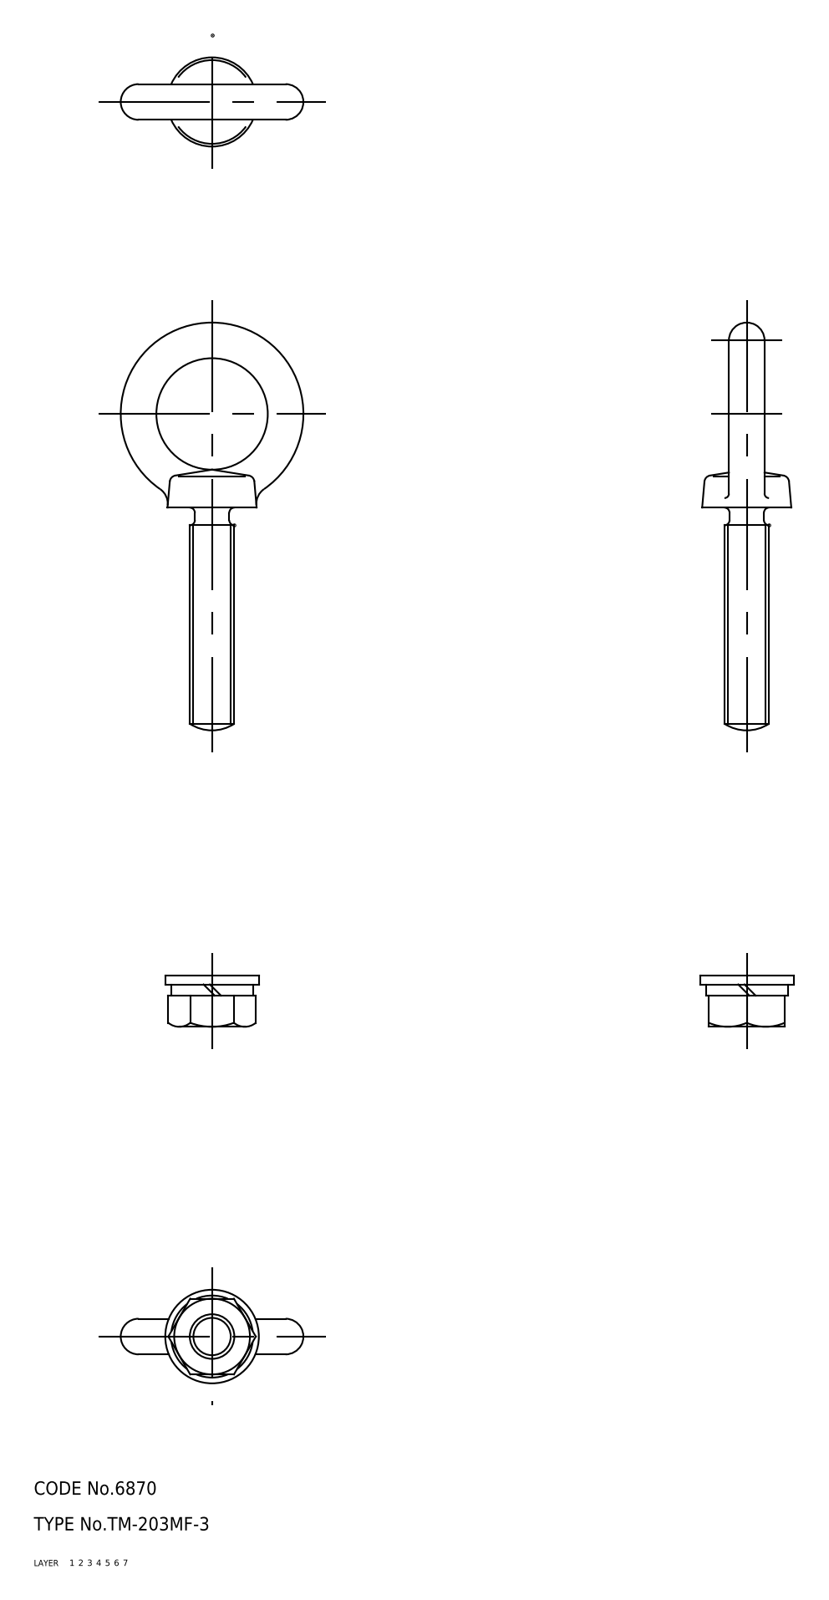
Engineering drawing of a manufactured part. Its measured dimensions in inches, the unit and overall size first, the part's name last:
Units: inches
Overall size (bounding box): 3.602 × 1.614 × 0.827
Round holes (diameter × count): ⌀0.394 ×1
Round bosses / shafts (diameter × count): ⌀0.827 ×1, ⌀0.724 ×1
Main face-to-face distances: 0.079, 0.098, 0.177, 0.669, 0.276, 0.374, 0.453
Volume: 0.776 in³ · Surface area: 10.73 in²
Bodies: 4 solids, 52 faces (13 planar, 12 cylindrical, 27 other)
Part name (STEP PRODUCT): TM_203MF_3
STEP written by: SolidWorks 2003240 (AUTOMOTIVE_DESIGN)
